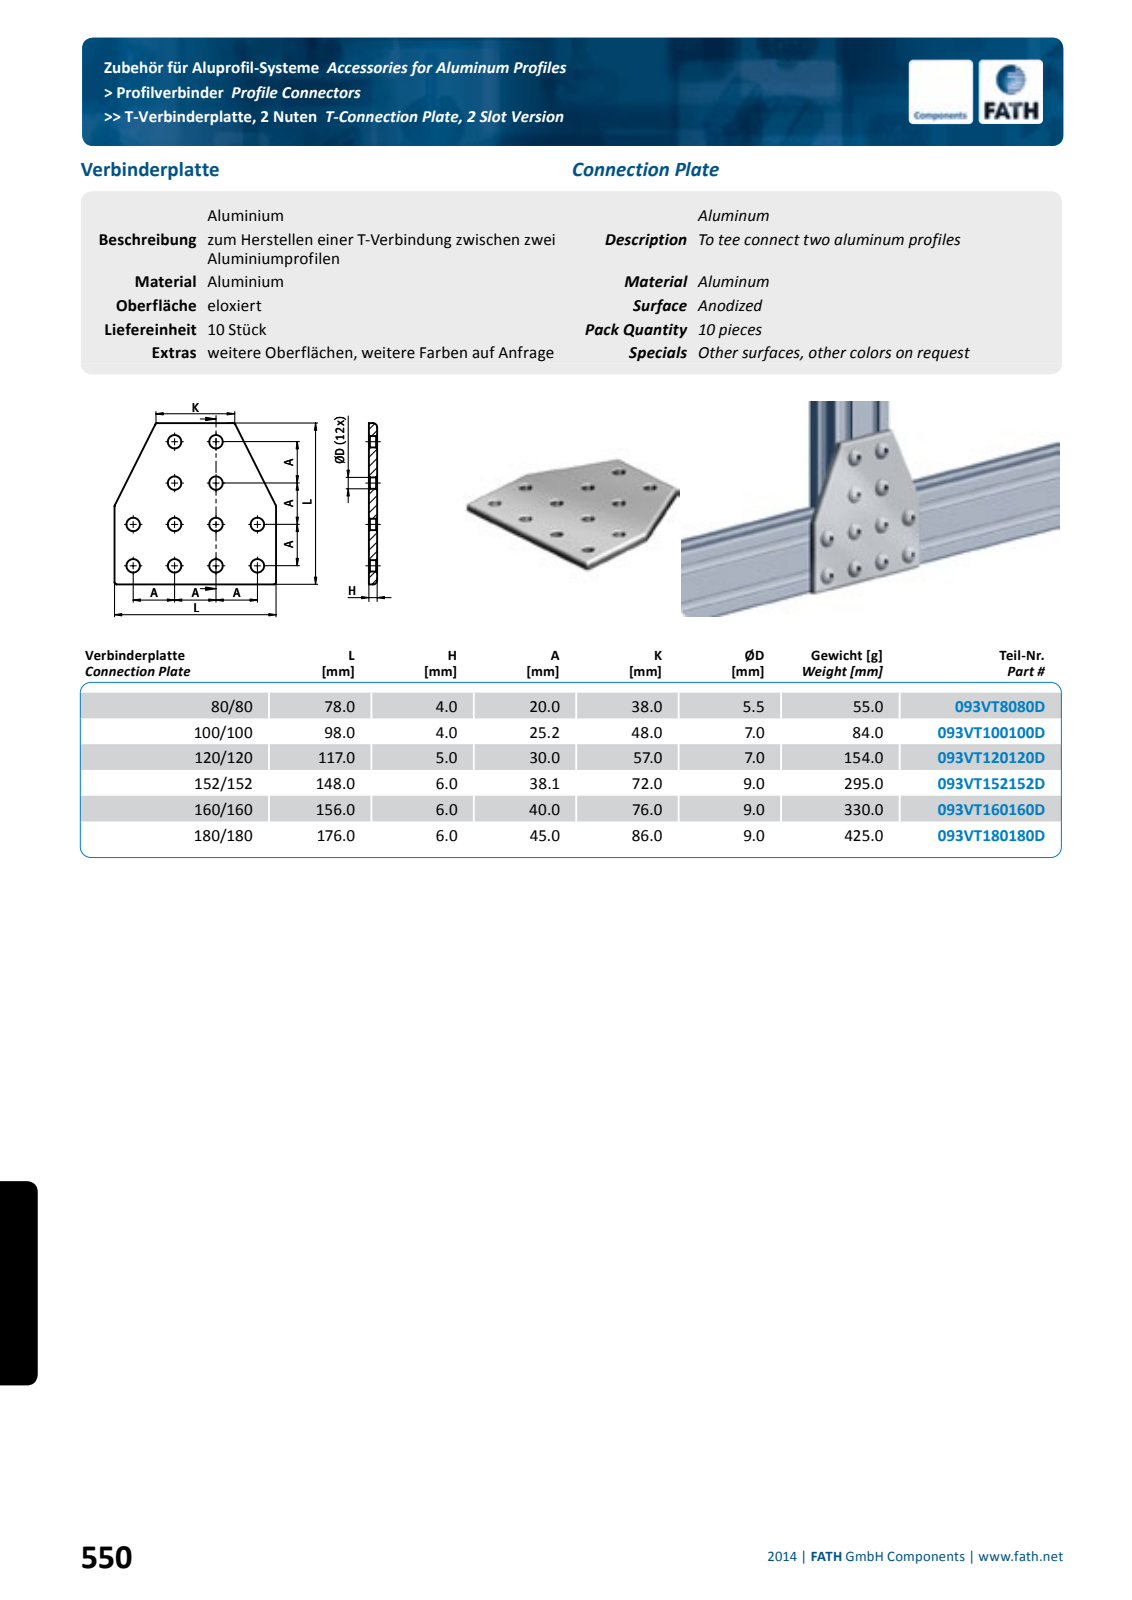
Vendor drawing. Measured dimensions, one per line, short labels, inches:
name: fath_093vt120120d
written by: Spatial InterOp 3D (automotive_design)
unit: in
bodies: 1 solid, 98 faces (8 planar, 36 cylindrical, 54 other)
size: 4.606 × 4.606 × 0.197
volume: 3.46 in³; area: 39.93 in²
holes: 12× ⌀0.276
rounds: 12× R0.079
face distances: 0.197, 4.606
hole spacings: 1.181, 2.641, 1.67, 2.362, 3.735, 3.341, 3.543, 4.259
